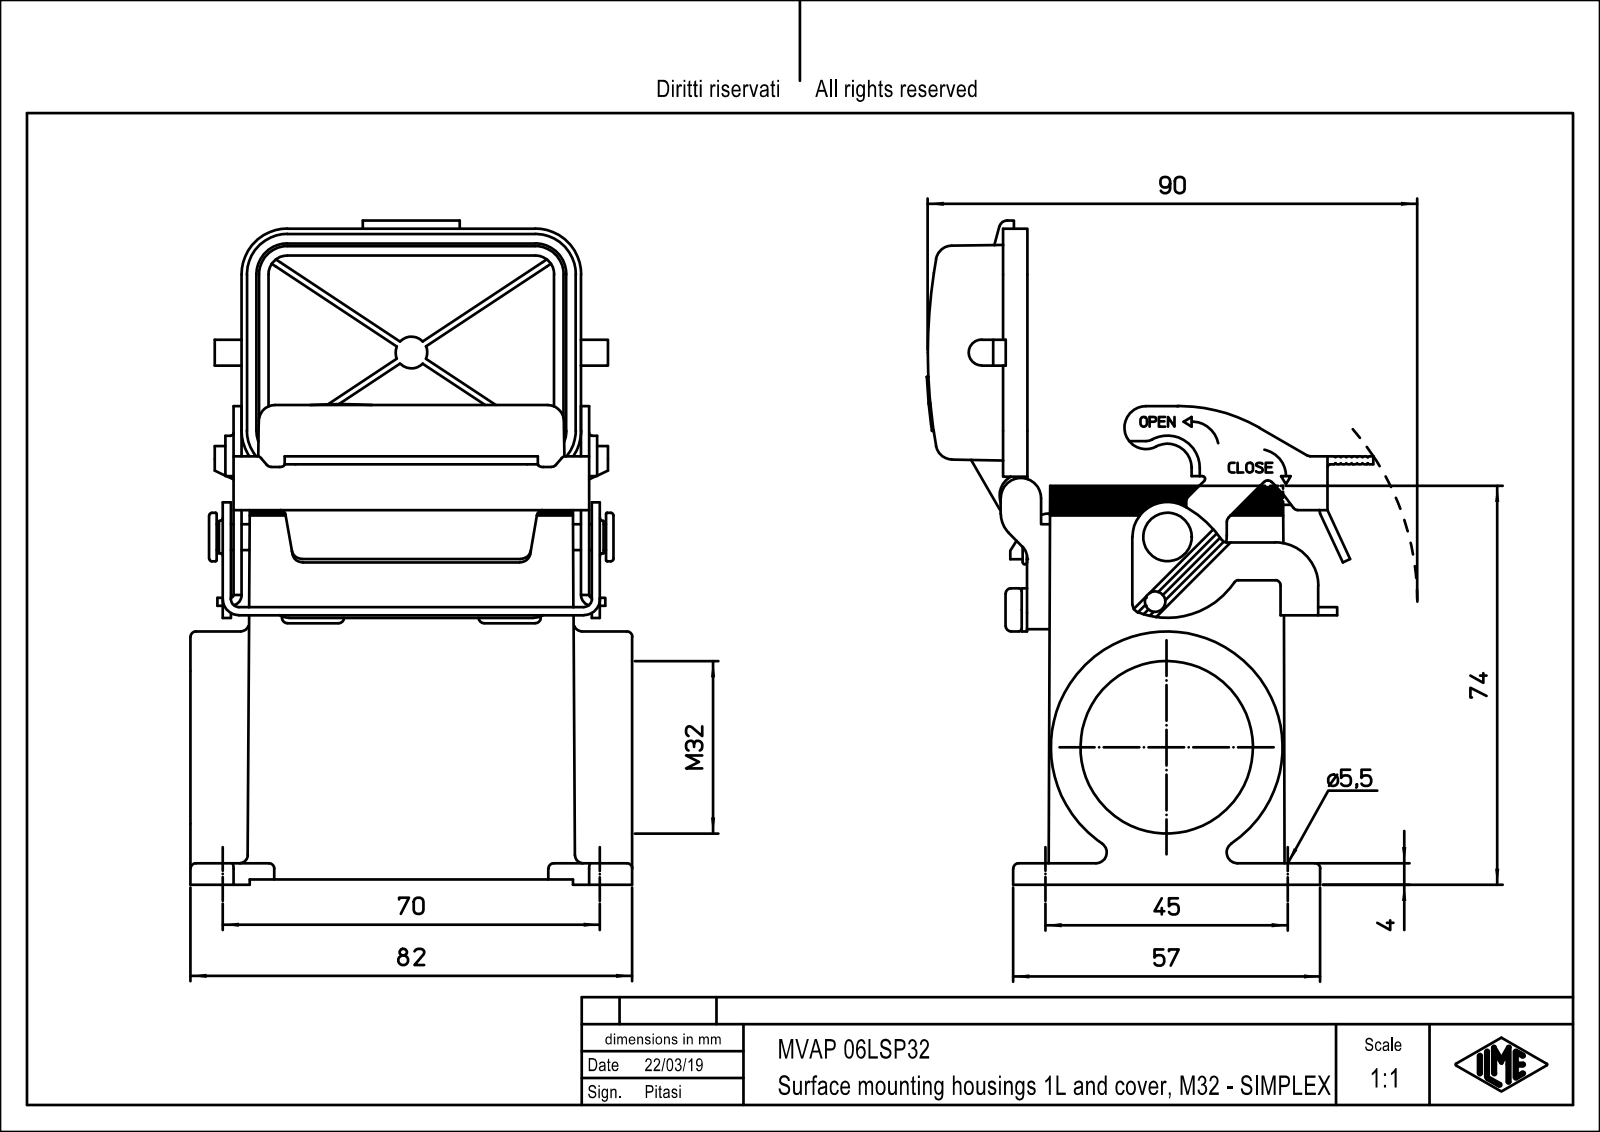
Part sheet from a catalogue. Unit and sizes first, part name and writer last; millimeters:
Units: millimetres
Overall size (bounding box): 122.72 × 82 × 79.9
Round holes (diameter × count): ⌀2.46 ×4, ⌀3 ×4, ⌀5.5 ×4, ⌀28 ×1, ⌀32 ×1
Round bosses / shafts (diameter × count): ⌀0.8 ×3, ⌀43 ×1, ⌀9 ×1, ⌀8.4 ×1, ⌀8 ×1, ⌀6 ×1, ⌀2.4 ×1
Partial cylindrical surfaces — rounded edges, fillets, slot ends (radius × count): R2 ×20, R3 ×15, R1.5 ×8, R3.5 ×7, R1 ×5, R6 ×5, R0.5 ×4, R1.8 ×4
Main face-to-face distances: 4, 40.5, 59.5, 44.5, 1.5, 36.5, 9.5, 13, 2, 47.75
Hole centre spacings: 15.81, 38.28, 57.71, 67.42, 27, 44, 45, 51.62
Volume: 119 025 mm³ · Surface area: 62 368 mm²
Bodies: 1 solid, 608 faces (383 planar, 201 cylindrical, 24 other)
Part name (STEP PRODUCT): MVAP_06_LSP32; MVAP_06LSP32.stp
STEP written by: PTC Creo Elements/Direct Modeling 19.0E 27-Jun-2016 (C) Parametric Technology GmbH (AUTOMOTIVE_DESIGN)
